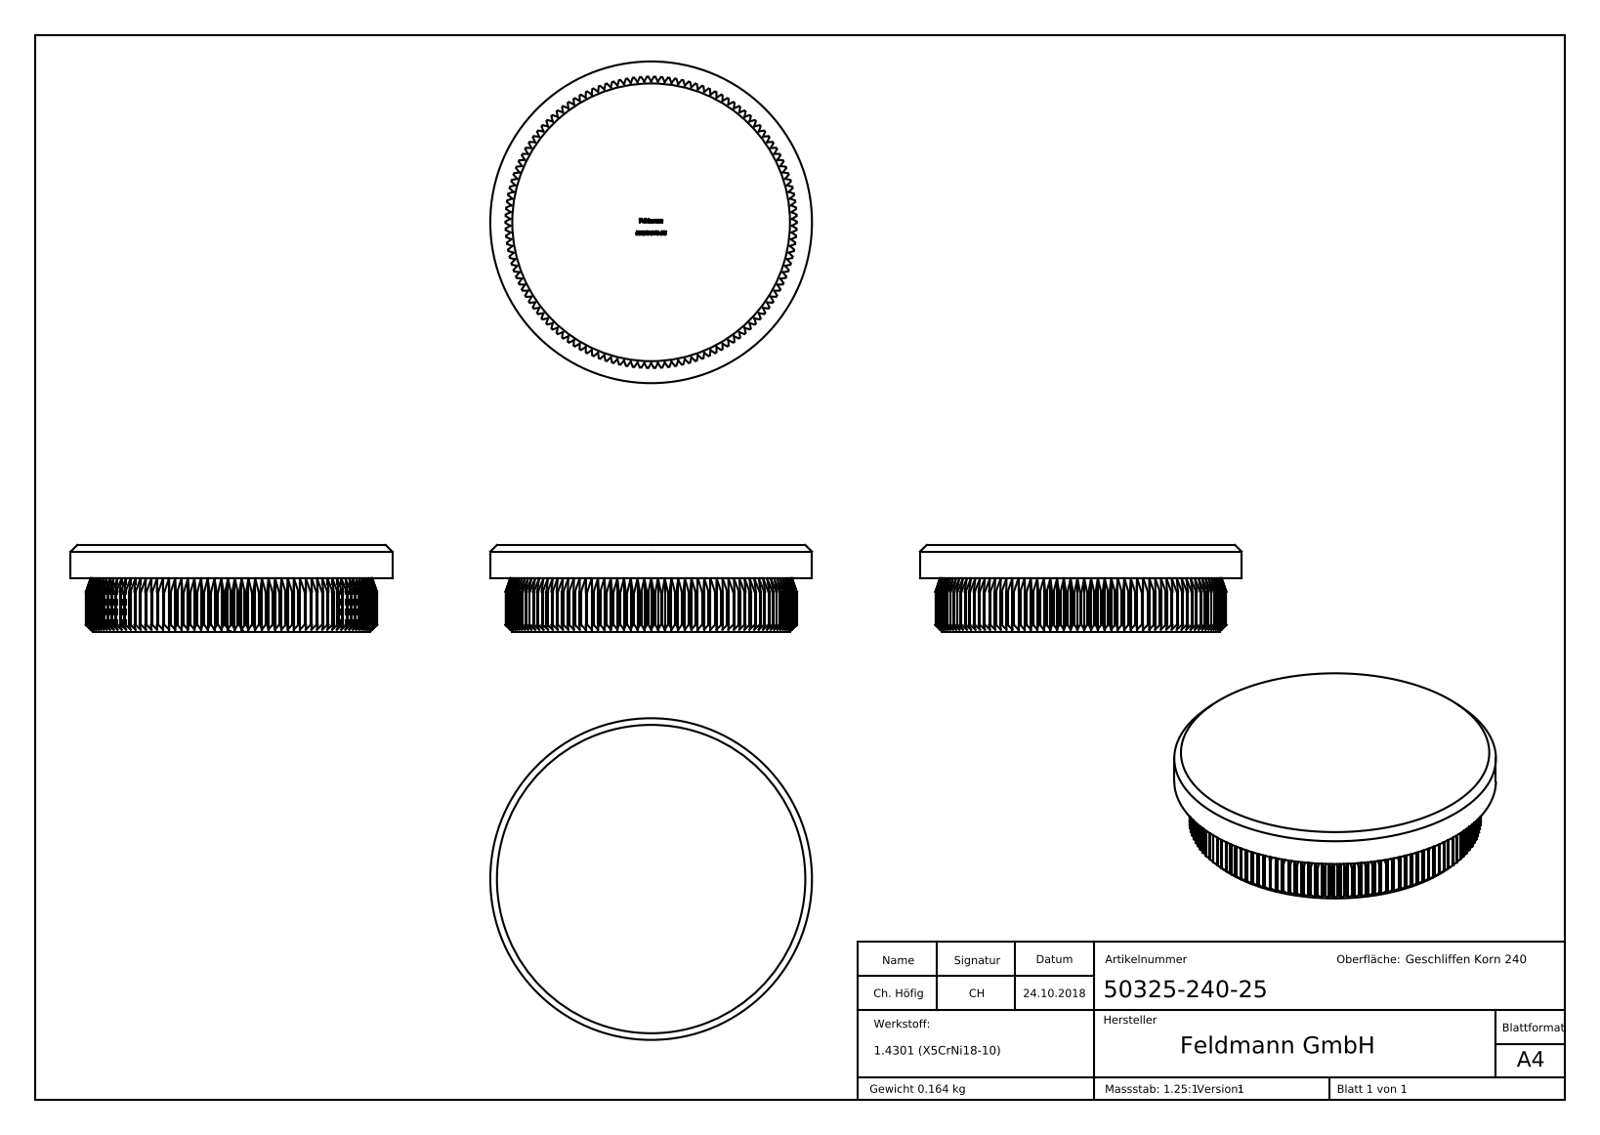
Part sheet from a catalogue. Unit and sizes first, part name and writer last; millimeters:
Units: millimetres
Overall size (bounding box): 48.3 × 48.3 × 13
Round bosses / shafts (diameter × count): ⌀48.3 ×1
Partial cylindrical surfaces — rounded edges, fillets, slot ends (radius × count): R21.85 ×1
Main face-to-face distances: 13, 8, 5, 21.16, 21.14, 21.18, 21.12, 7.9, 12.9, 1.64
Volume: 20 706 mm³ · Surface area: 6 103 mm²
Bodies: 1 solid, 782 faces (401 planar, 132 cylindrical, 249 other)
Part name (STEP PRODUCT): 50325-240-25
STEP written by: SolidWorks 2015 (CONFIG_CONTROL_DESIGN)
